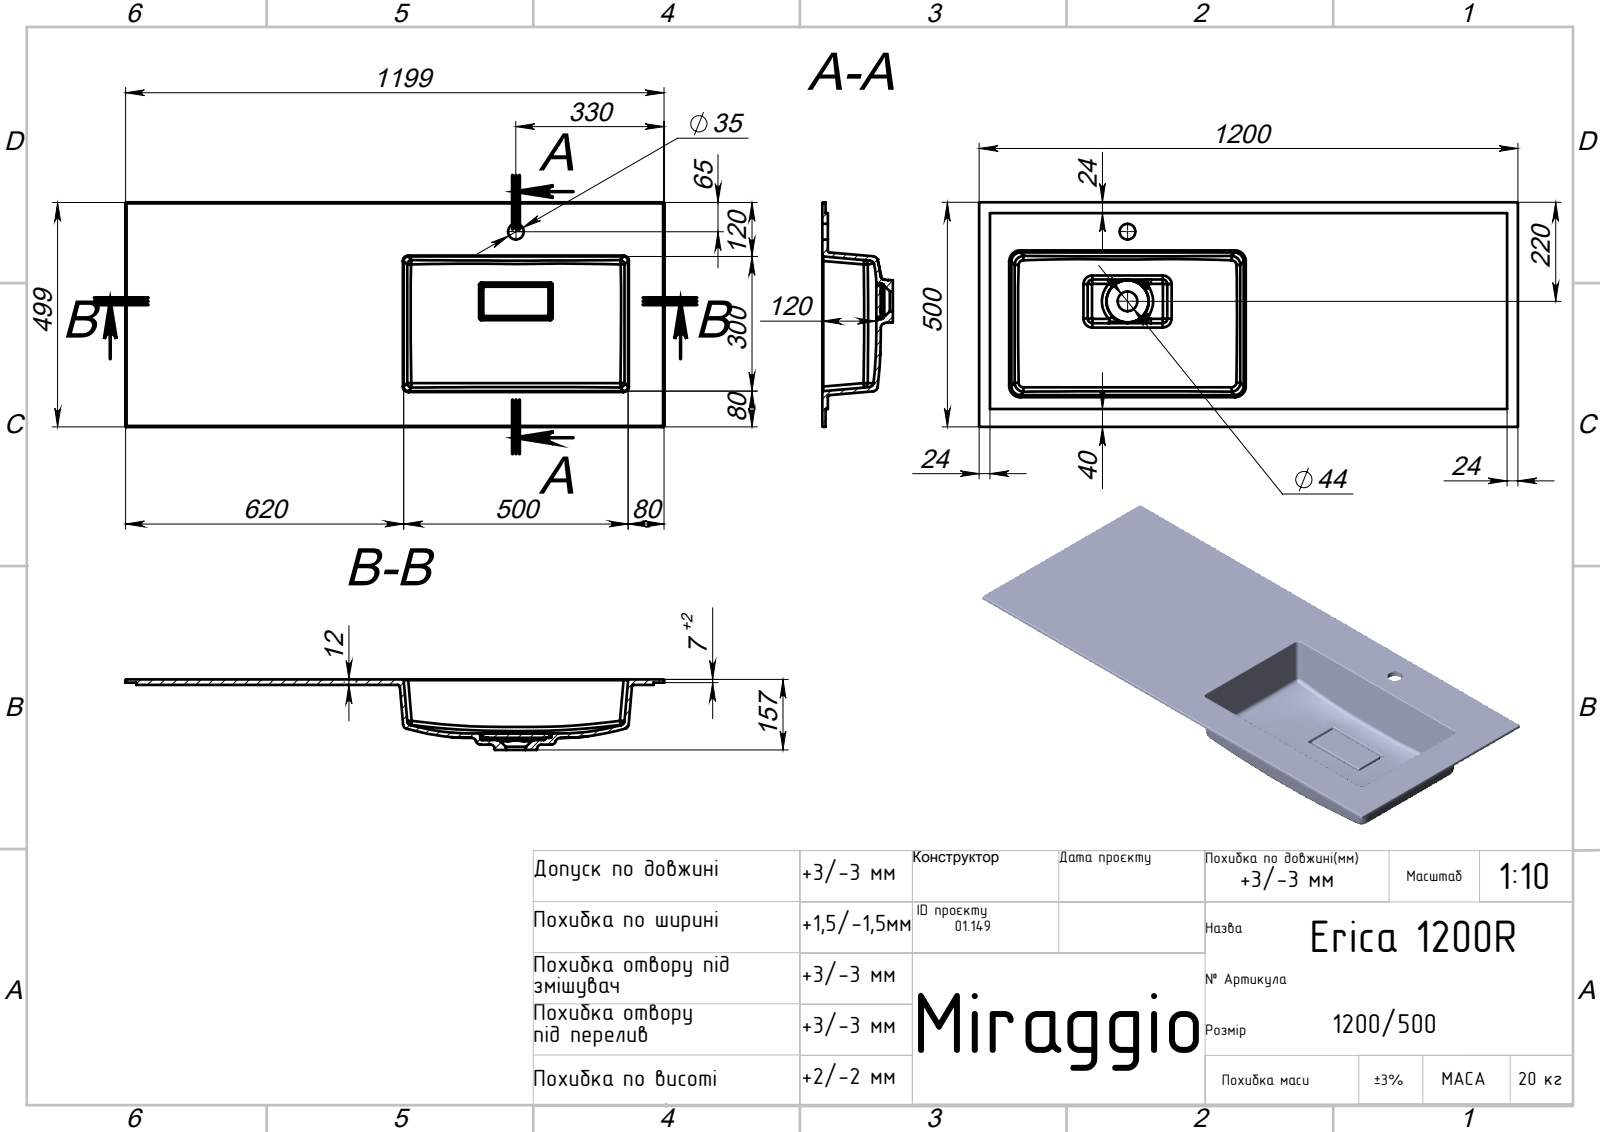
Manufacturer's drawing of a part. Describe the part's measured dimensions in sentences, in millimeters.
The part is named "Erica 1200R". Its 3-D file was written by "SolidWorks 2020 (AUTOMOTIVE_DESIGN)". It is 2 solids with 244 faces: 44 planar, 69 cylindrical and 131 other. Overall it measures 1200 by 500 by 157 millimeters. Its volume is 8 197 000 cubic millimeters and its surface area 1 562 000 square millimeters. Round holes: 1 of diameter 35. Partial cylindrical surfaces (rounded edges, fillets, slot ends): 26 of radius 2, 18 of radius 3, 6 of radius 6, 4 of radius 5, 4 of radius 10, 4 of radius 20. The main face-to-face distances are 12, 5, 10, 7, 9.99, 123, 118, 130, 108, 113.
